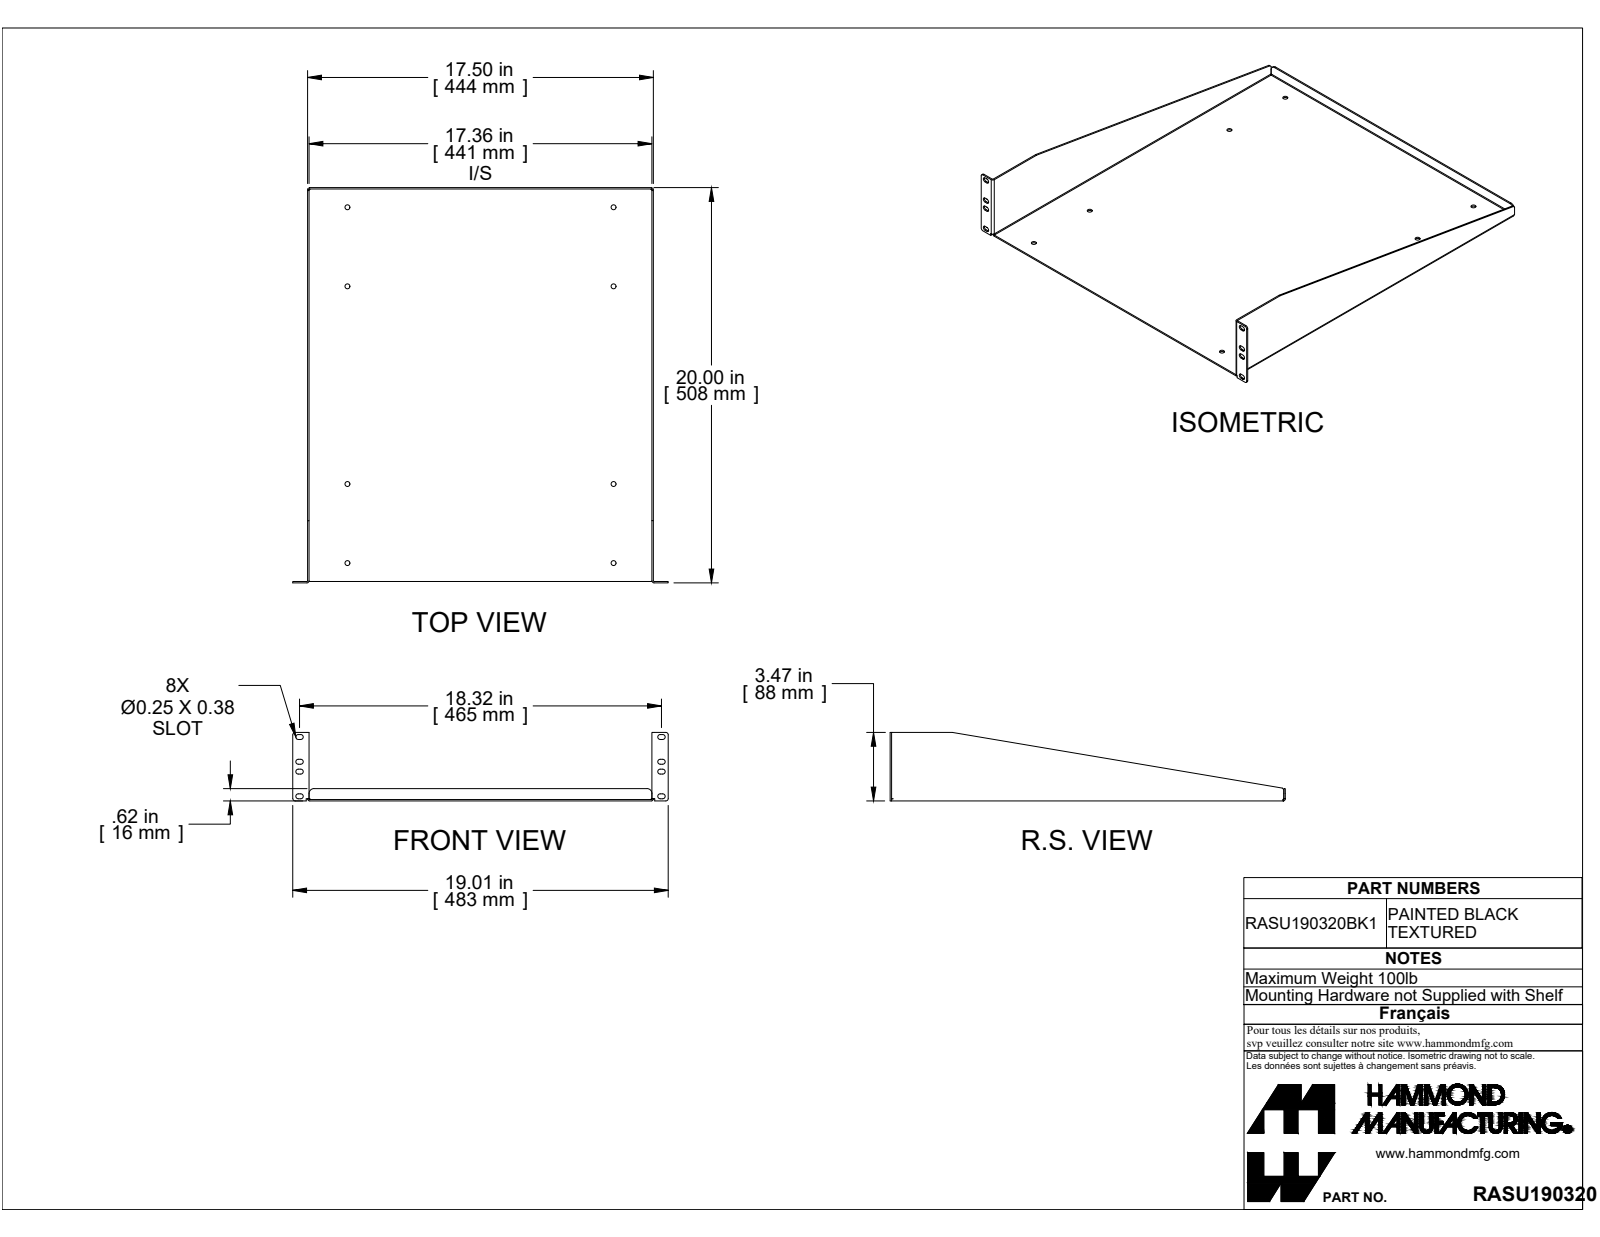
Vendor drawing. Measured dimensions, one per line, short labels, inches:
name: RASU190320BK1
written by: SolidWorks 2019 (CONFIG_CONTROL_DESIGN)
unit: in
bodies: 1 solid, 104 faces (56 planar, 44 cylindrical, 4 other)
size: 20 × 19.006 × 3.468
volume: 32.28 in³; area: 904 in²
holes: 8× ⌀0.25
rounds: 20× R0.125, 5× R0.036, 5× R0.108, 3× R0.055, 2× R0.25
face distances: 0.072, 17.428, 17.356, 17.5, 19.856, 19.928, 0.072, 19.928, 20, 0.625
hole spacings: 4, 13.468, 14, 14.049, 19.426, 10, 16.774, 18
